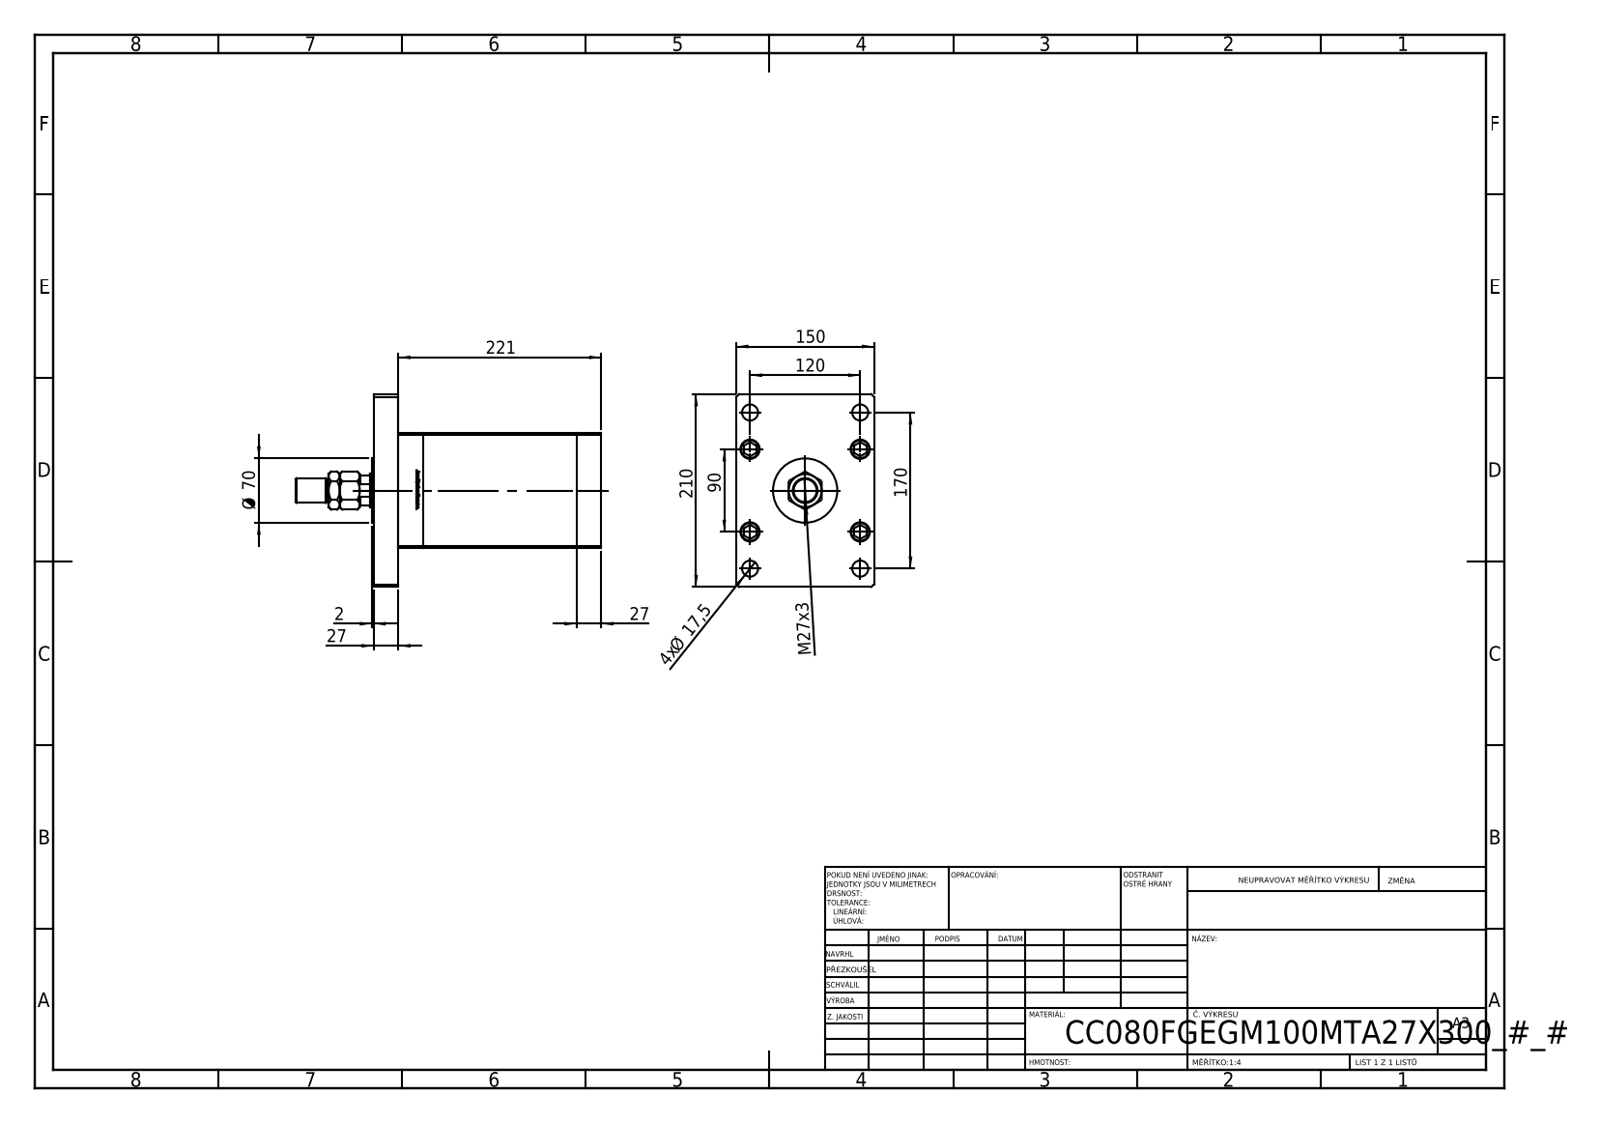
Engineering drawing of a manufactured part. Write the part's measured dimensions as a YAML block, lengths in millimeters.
part_name: "V220C_F_MIDDLE; MTA; V220C_FRONT_F; V220C_VC_F (+3 more)"
step_written_by: "SolidWorks 2019 (CONFIG_CONTROL_DESIGN)"
units: millimeters
bodies: {solids: 20, faces: 1359, planar: 532, cylindrical: 191, other: 636}
overall_size: [333, 210, 150]
volume: 4421000
surface_area: 481544
round_holes:
  - {diameter: 17.5, count: 9}
  - {diameter: 22, count: 5}
  - {diameter: 16, count: 4}
  - {diameter: 21, count: 4}
  - {diameter: 2, count: 2}
  - {diameter: 13.16, count: 2}
  - {diameter: 25.5, count: 1}
  - {diameter: 36, count: 1}
  - {diameter: 37.5, count: 1}
round_bosses_or_shafts:
  - {diameter: 8, count: 9}
  - {diameter: 21, count: 5}
  - {diameter: 80, count: 1}
  - {diameter: 70, count: 1}
  - {diameter: 27, count: 1}
  - {diameter: 25, count: 1}
partial_cylinders:
  - {radius: 0.93, count: 2}
  - {radius: 17.5, count: 1}
face_to_face_distances: [27, 194, 221, 150, 125, 167, 54, 248, 33.5, 6.5]
hole_center_spacings: [51, 40, 75, 104.04, 120, 126.49, 130, 176.92]
